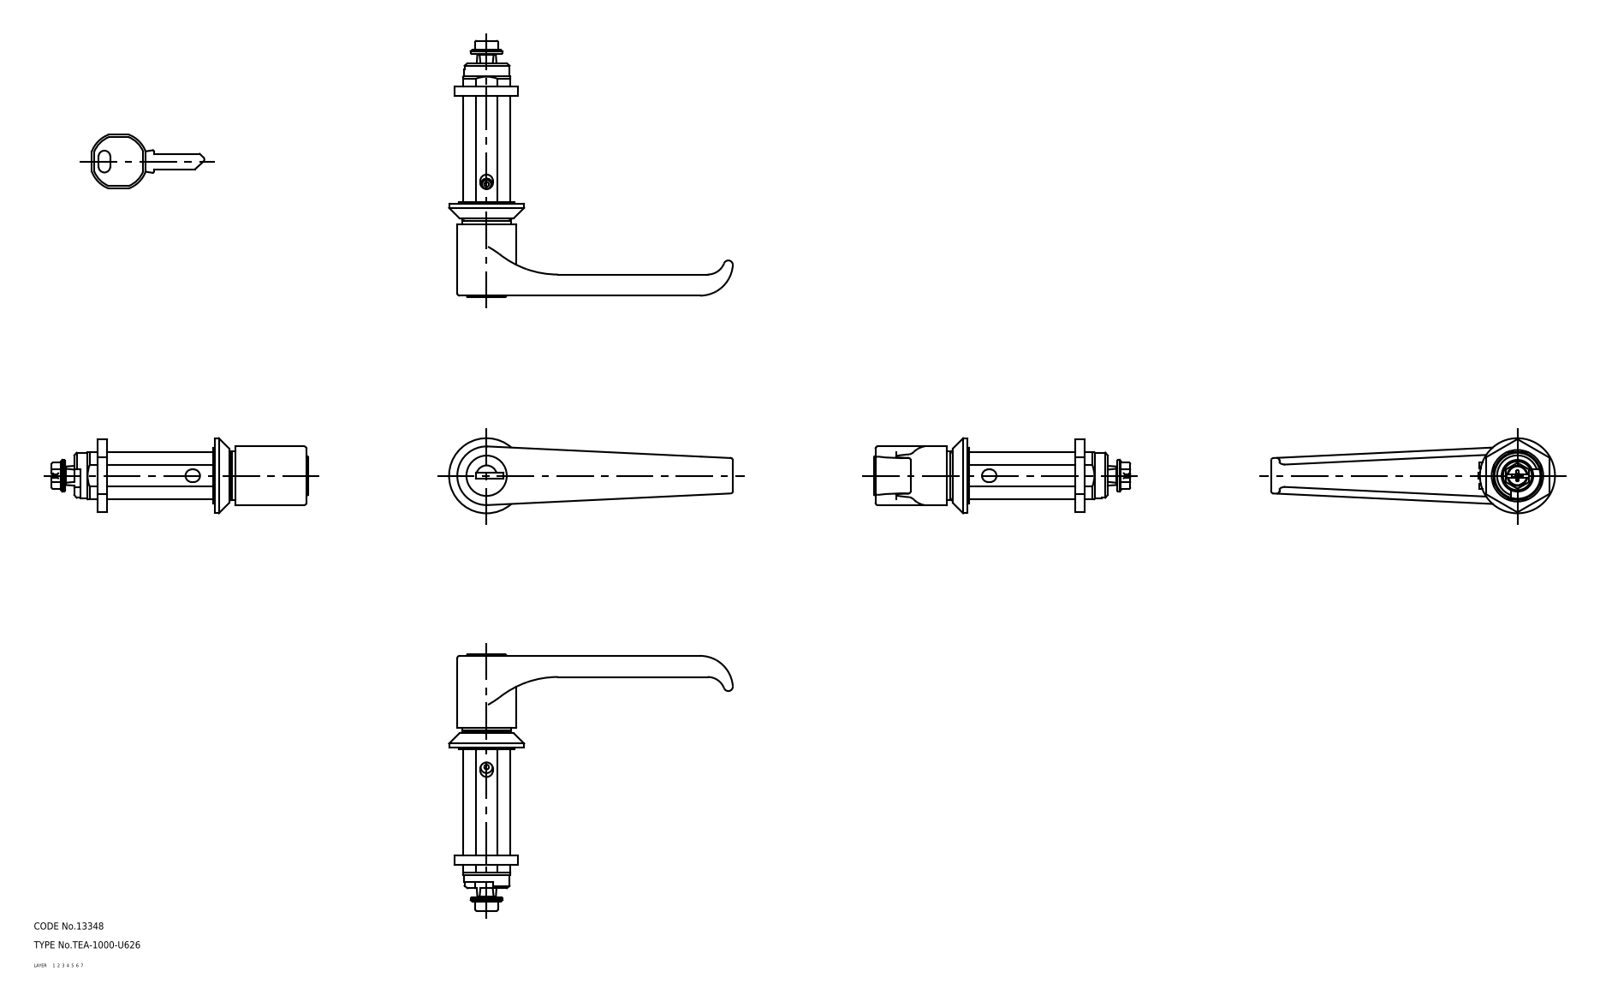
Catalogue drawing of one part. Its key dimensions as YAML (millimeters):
part_name: "nut; lock; key; housing (+2 more)"
step_written_by: "CADfix (AUTOMOTIVE_DESIGN)"
units: millimeters
bodies: {solids: 5, faces: 359, planar: 0, cylindrical: 0, other: 359}
overall_size: [173.41, 120.96, 32]
volume: 53362
surface_area: 27498
